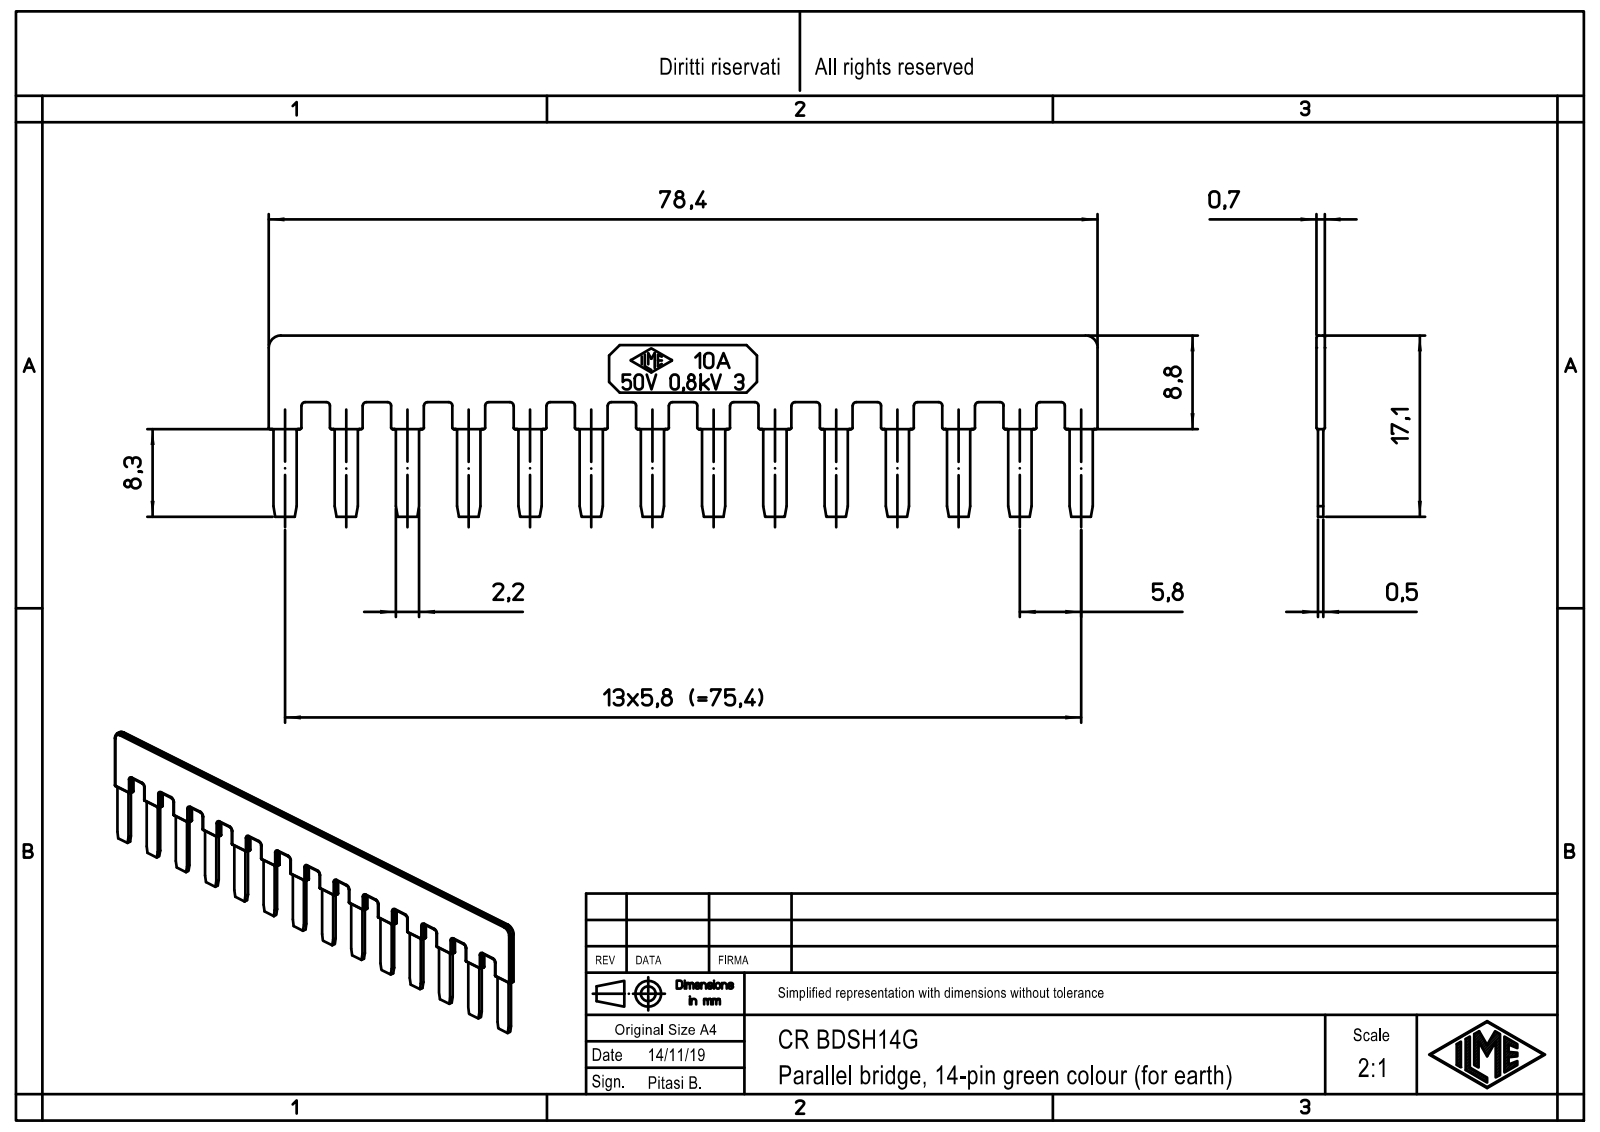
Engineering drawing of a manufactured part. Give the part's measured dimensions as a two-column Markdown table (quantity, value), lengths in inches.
| quantity | value |
| --- | --- |
| part name | PONTE_14G |
| STEP written by | Creo Elements/Direct Modeling 20.1B 02-Apr-2019 (C) Parametric Technology GmbH (AUTOMOTIVE_DESIGN) |
| units | inches |
| bodies | 1 solid, 470 faces (162 planar, 196 cylindrical, 112 other) |
| overall size | 3.091 × 0.675 × 0.031 |
| volume | 0.037 in³ |
| surface area | 3.071 in² |
| partial cylindrical surfaces (radius × count) | 0.008 × 60, 0.004 × 30, 0.006 × 28, 0.014 × 26, 0.045 × 2 |
| main face-to-face distances | 0.031, 0.026, 0.02, 0.228, 0.457, 0.685, 0.913, 0.087, 1.142, 0.142 |
